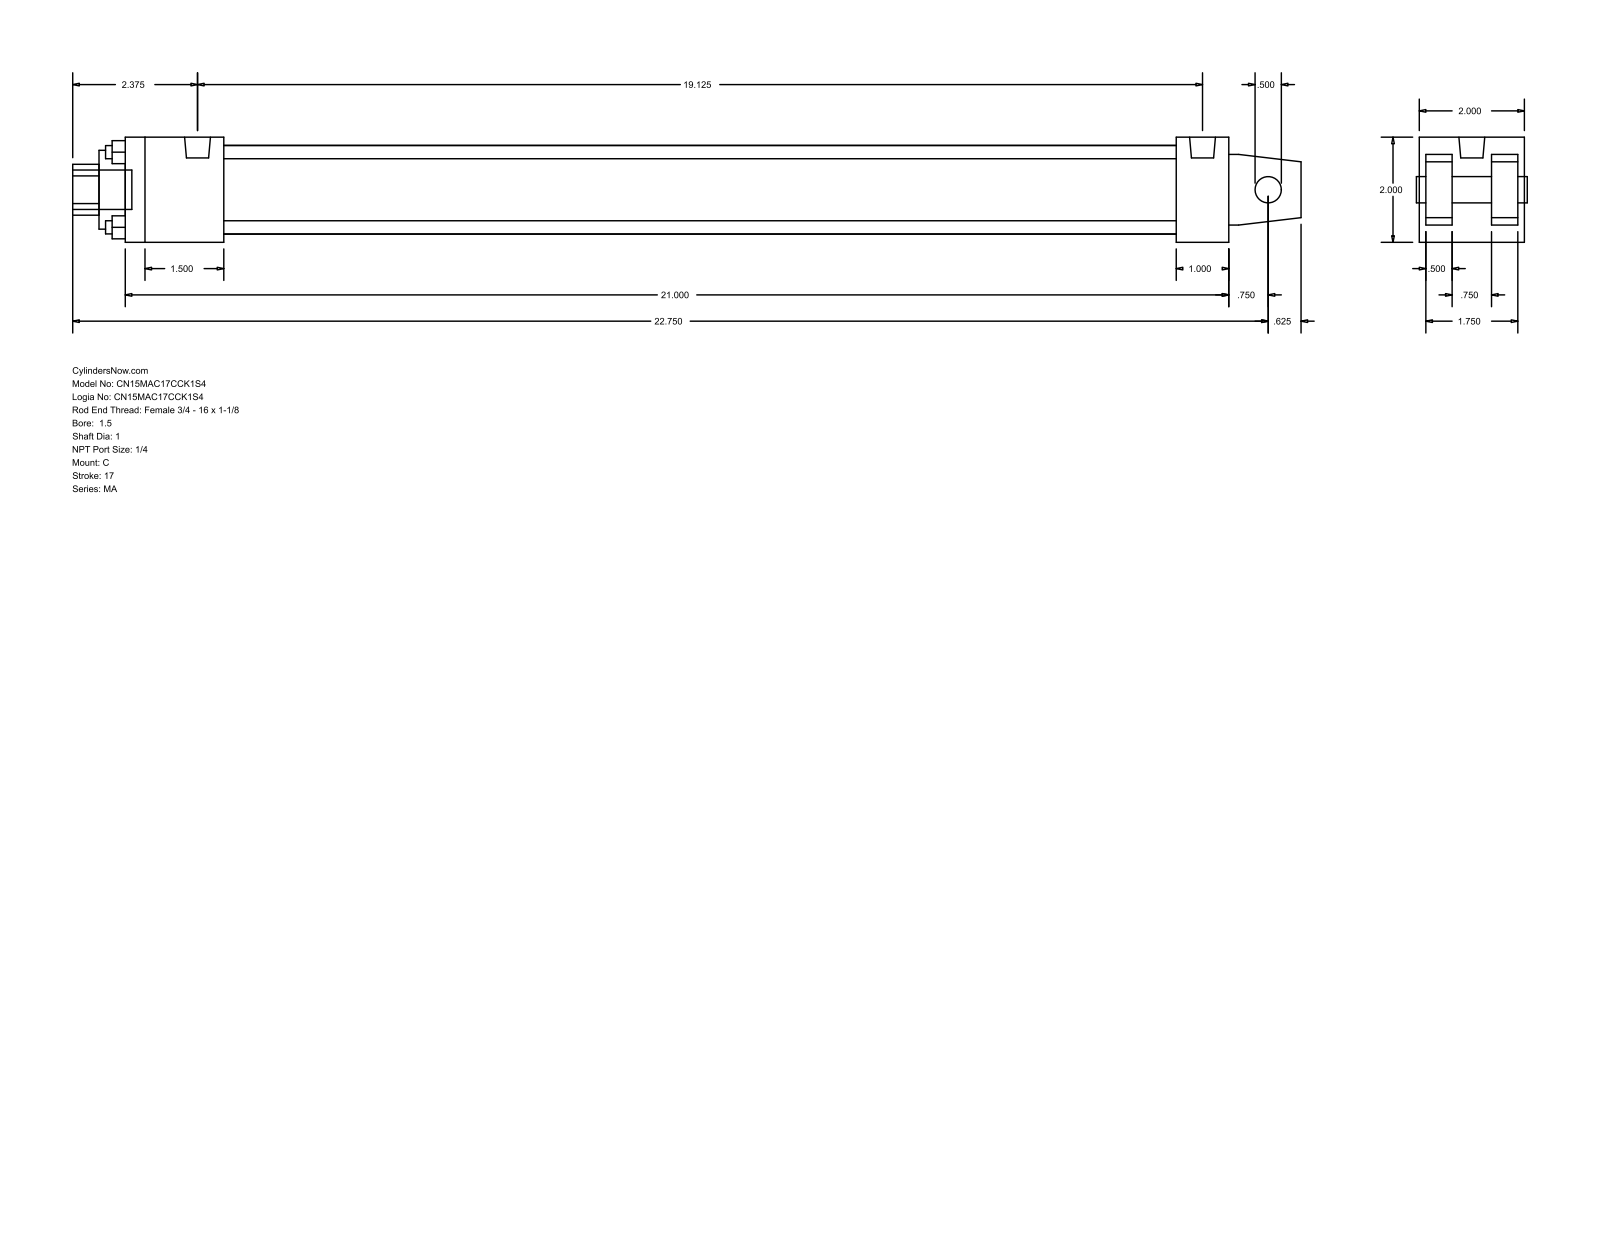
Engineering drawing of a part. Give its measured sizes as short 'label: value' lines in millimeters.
name: MA_C__0150_1
written by: GSSL Pune (CONFIG_CONTROL_DESIGN)
unit: mm
bodies: 0 solids, 103 faces (76 planar, 27 cylindrical, 0 other)
size: 593.73 × 50.8 × 50.8
holes: 4× ⌀6.35, 1× ⌀12.7, 1× ⌀25.4, 1× ⌀38.1, 1× ⌀42.93
bosses: 4× ⌀7.94, 2× ⌀12.49, 1× ⌀19.05
rounds: 1× R12.29
face distances: 50.8, 47.63, 12.7, 34.93, 3.17, 15.87, 31.76, 60.33, 520.7, 44.46
hole spacings: 25.68, 36.32, 51.36
